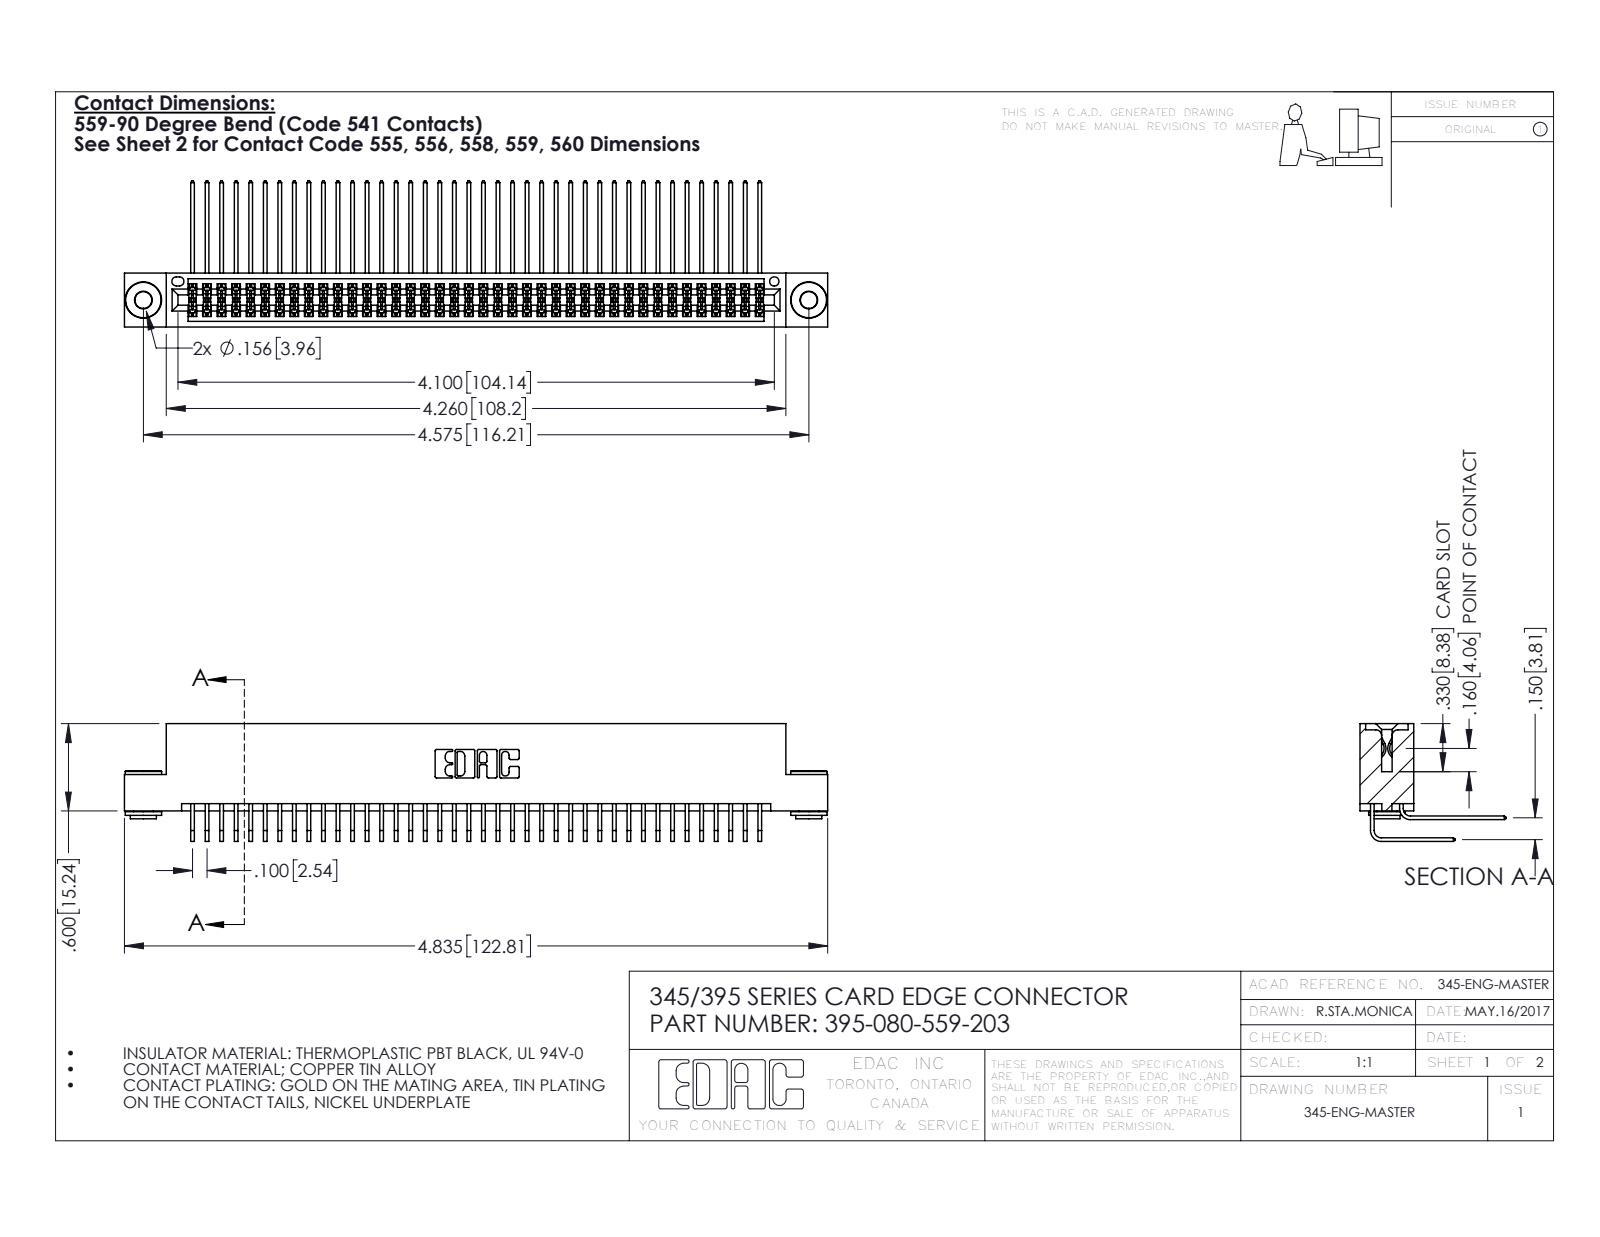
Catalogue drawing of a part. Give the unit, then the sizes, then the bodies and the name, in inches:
Units: inches
Overall size (bounding box): 4.835 × 1.005 × 0.809
Round holes (diameter × count): ⌀0.116 ×2, ⌀0.156 ×2, ⌀0.064 ×1
Round bosses / shafts (diameter × count): ⌀0.25 ×2, ⌀0.18 ×2, ⌀0.136 ×2
Partial cylindrical surfaces — rounded edges, fillets, slot ends (radius × count): R0.006 ×120, R0.01 ×22, R0.007 ×6, R0.031 ×6, R0.026 ×3, R0.014 ×2, R0.019 ×2, R0.022 ×2
Main face-to-face distances: 0.072, 0.298, 0.2, 0.37, 0.025, 0.098, 0.272, 0.225, 0.175, 0.15
Hole centre spacings: 0.27, 4.339, 4.575
Volume: 0.756 in³ · Surface area: 32.01 in²
Bodies: 83 solids, 4324 faces (2890 planar, 1426 cylindrical, 8 other)
Part name (STEP PRODUCT): 345-250-002_345-250-002-102; 345 Part_Flush Mounting Lugs - 0.156 Dia-TH; 345-292-001_558 559 Tail - 1; 345-292-001_559 Tail - 2 (+1 more)
STEP written by: SolidWorks 2016 (CONFIG_CONTROL_DESIGN)
